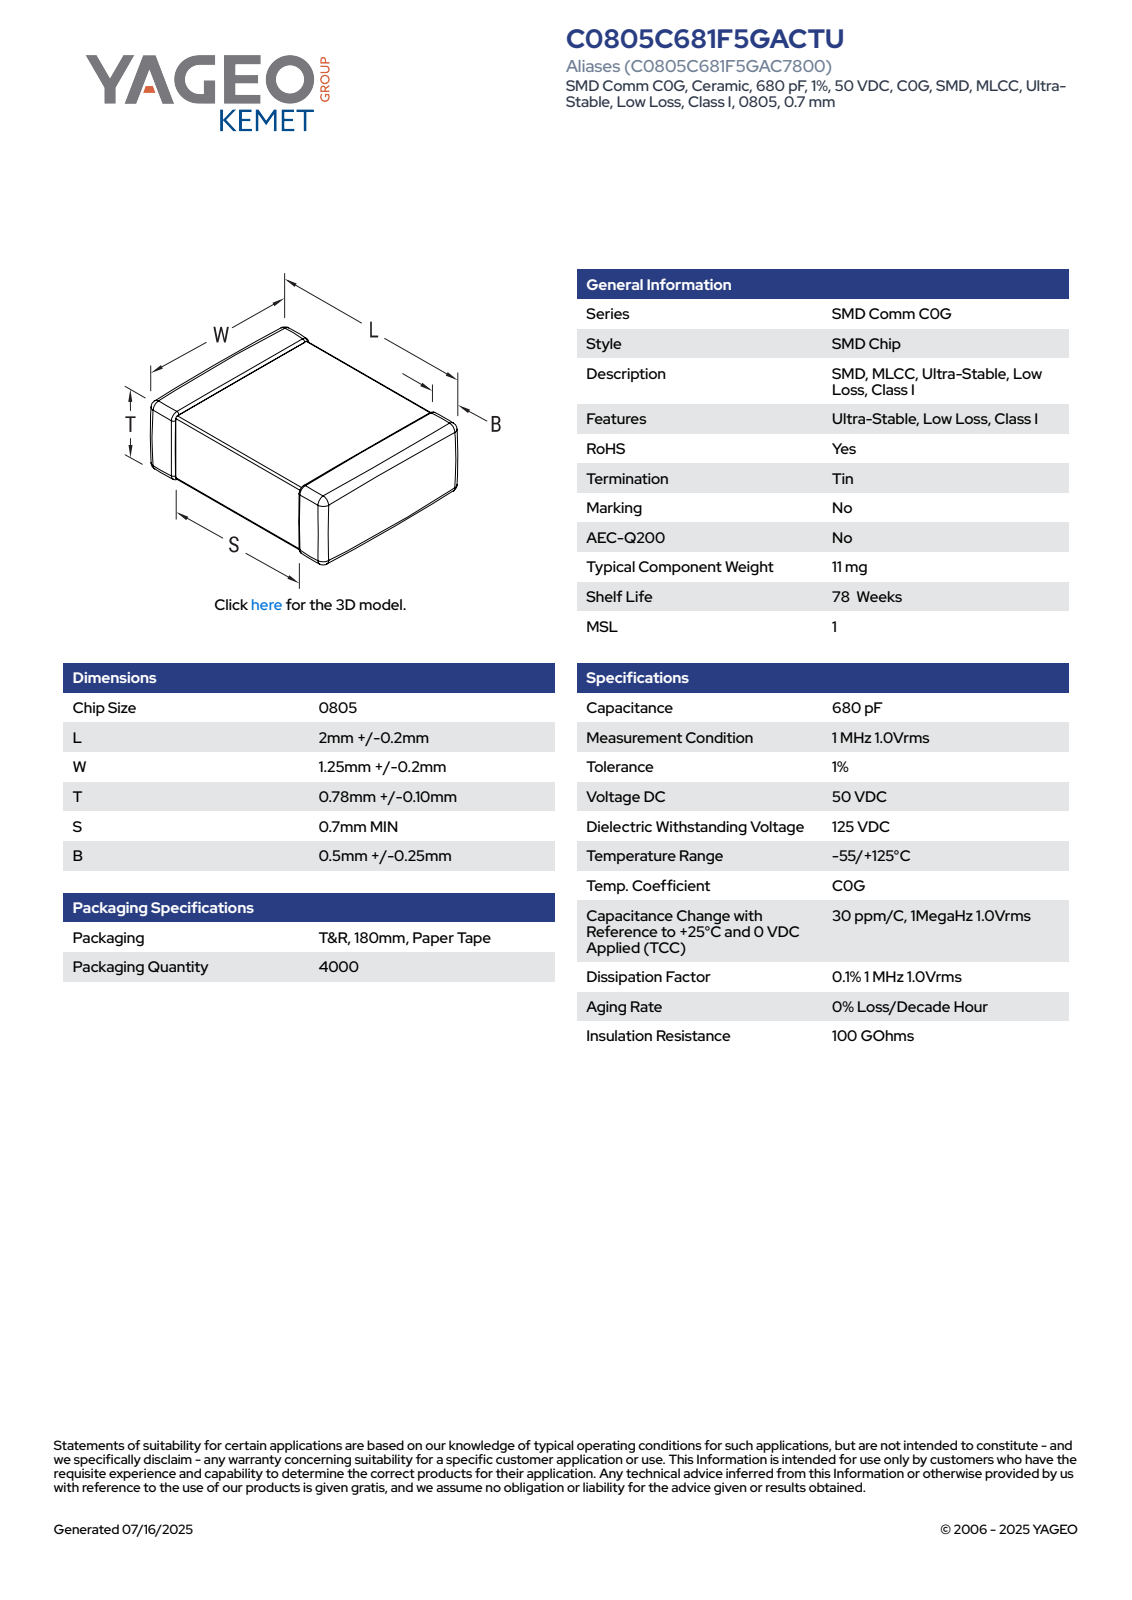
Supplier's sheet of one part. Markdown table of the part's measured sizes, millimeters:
| quantity | value |
| --- | --- |
| part name | CCS_CCSTD_0805_L2.2W1.45T0.88B0.5 |
| STEP written by | SolidWorks 2021 (AUTOMOTIVE_DESIGN) |
| units | millimeters |
| bodies | 4 solids, 121 faces (71 planar, 34 cylindrical, 16 other) |
| overall size | 2.2 × 1.45 × 0.88 |
| volume | 3 mm³ |
| surface area | 13 mm² |
| main face-to-face distances | 0.85, 0.88, 2.2, 1.45, 1.42, 0.82, 1.39, 0.97, 1.23, 1.19 |
